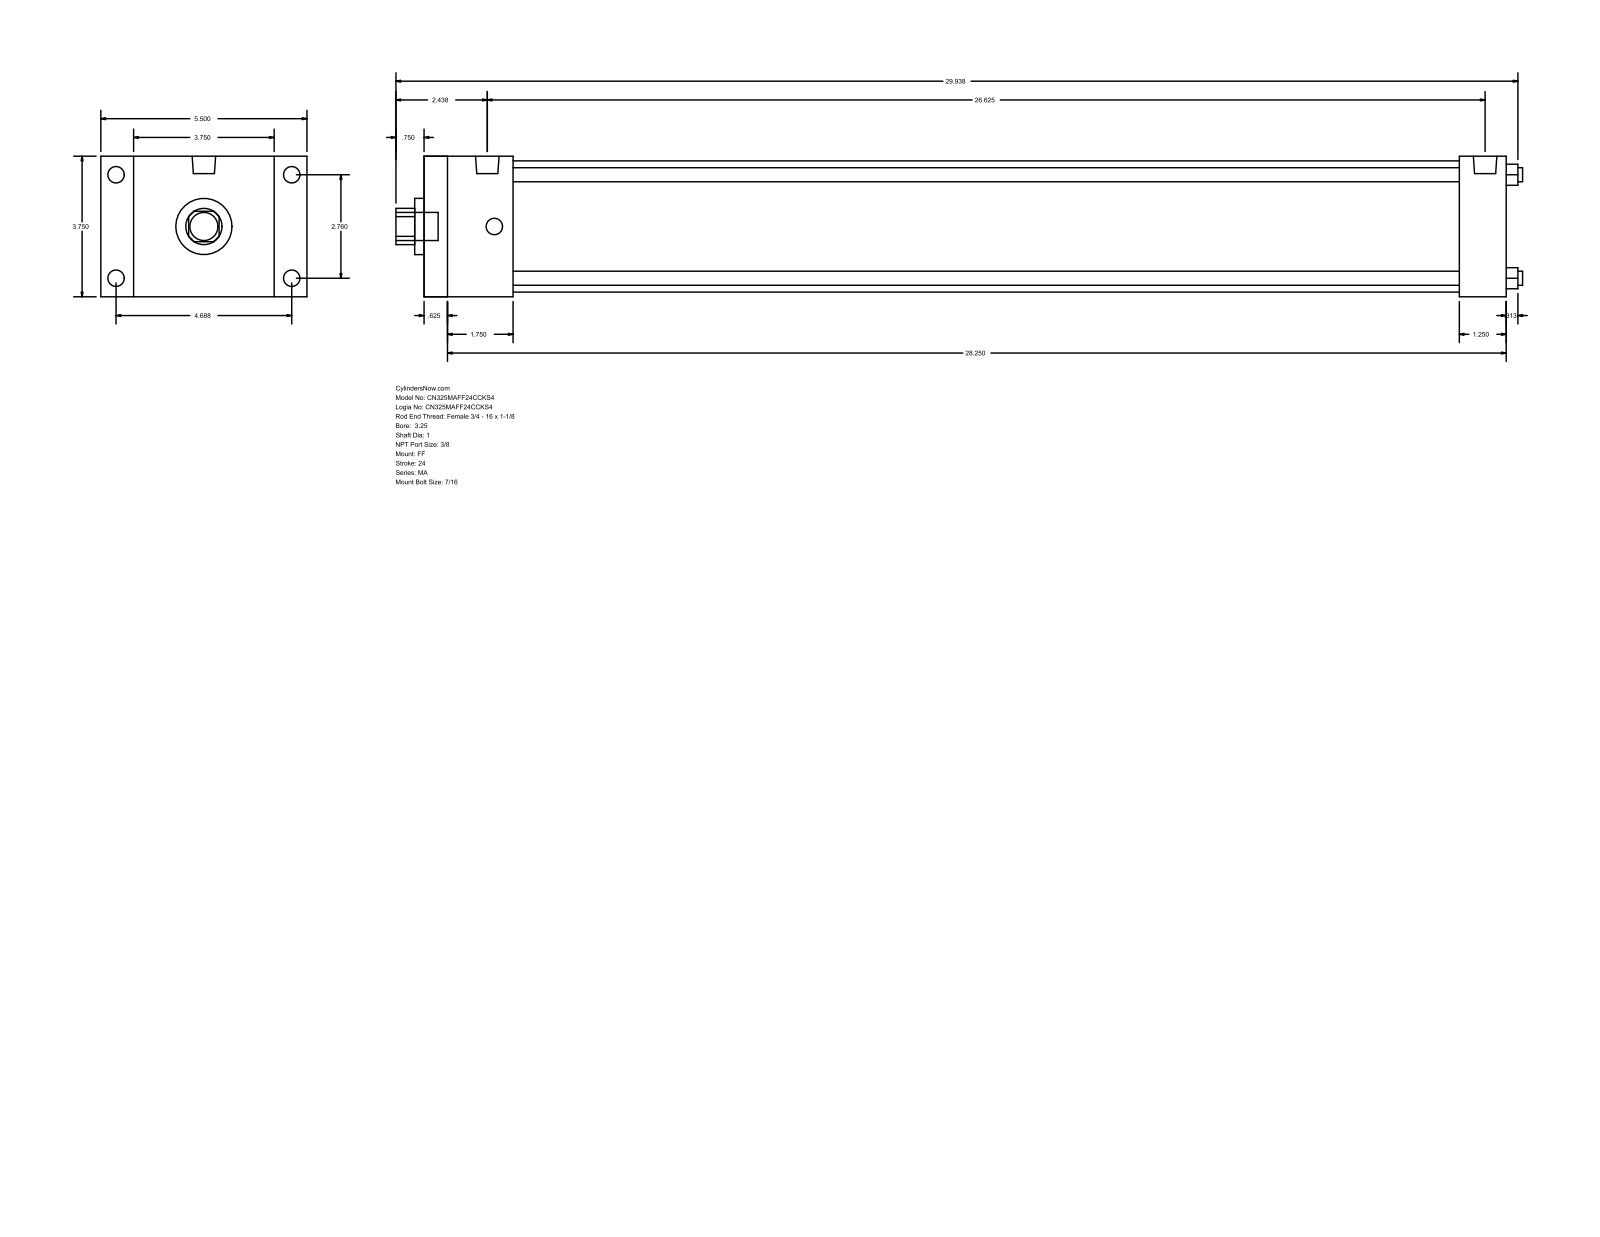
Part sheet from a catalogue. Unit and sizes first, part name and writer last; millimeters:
Units: millimetres
Overall size (bounding box): 763.59 × 139.7 × 95.25
Round holes (diameter × count): ⌀9.53 ×4, ⌀25.4 ×1, ⌀38.1 ×1, ⌀88.9 ×1
Round bosses / shafts (diameter × count): ⌀11.11 ×8, ⌀15.93 ×2, ⌀19.05 ×1
Partial cylindrical surfaces — rounded edges, fillets, slot ends (radius × count): R12.29 ×1
Main face-to-face distances: 95.24, 733.43, 15.87, 717.56, 22.23, 117.47, 60.33, 701.68, 44.46, 685.81
Hole centre spacings: 49.57, 70.1, 99.14
Bodies: 0 solids, 92 faces (64 planar, 28 cylindrical, 0 other)
Part name (STEP PRODUCT): MA_FF__0325_1
STEP written by: GSSL Pune (CONFIG_CONTROL_DESIGN)
